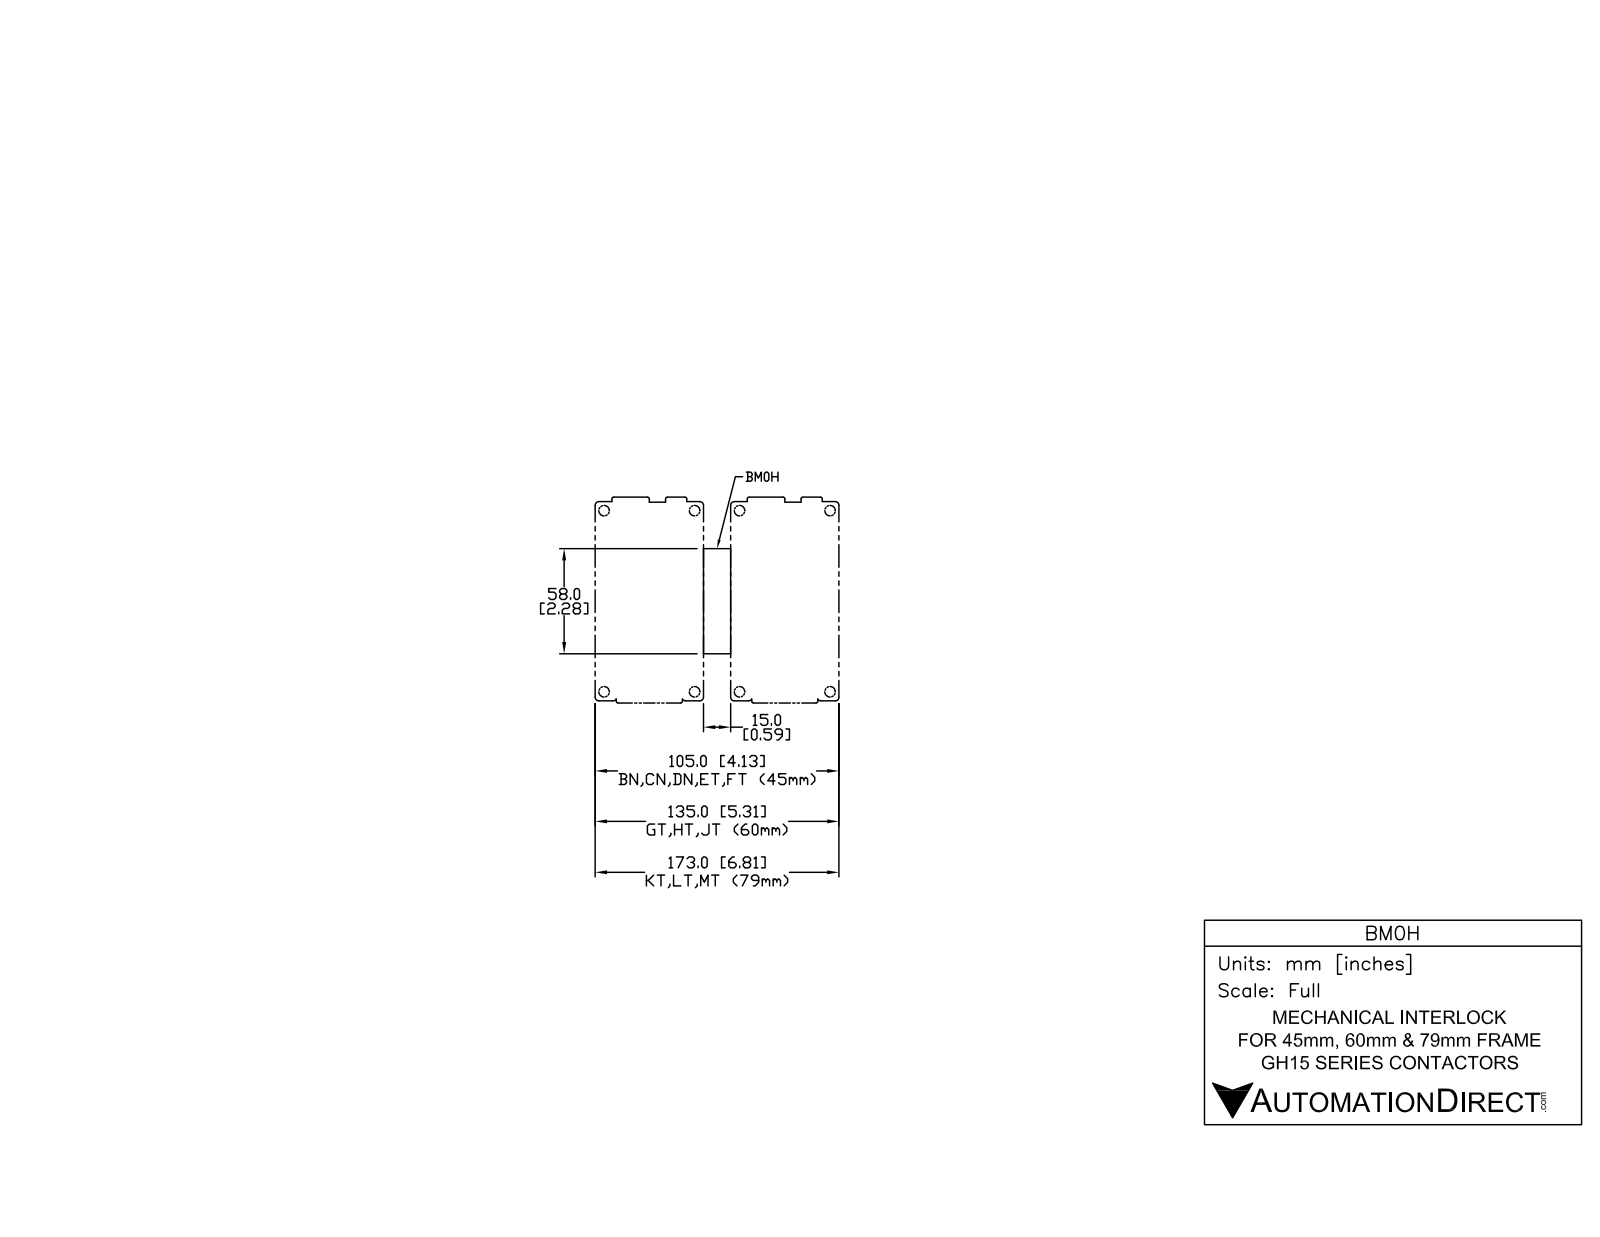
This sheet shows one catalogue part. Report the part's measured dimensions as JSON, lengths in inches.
{"part_name": "BM0H", "step_written_by": "SolidWorks 2009 (AUTOMOTIVE_DESIGN)", "units": "inches", "bodies": {"solids": 1, "faces": 82, "planar": 58, "cylindrical": 20, "other": 4}, "overall_size": [2.303, 1.929, 0.827], "volume_in3": 2.485, "surface_area_in2": 15.91, "round_bosses_or_shafts": [[0.276, 1], [0.118, 1]], "partial_cylinders_radius": [[0.02, 4], [0.206, 2], [0.207, 2]], "face_to_face_distances": [0.591, 1.929, 2.303, 0.118, 0.197, 0.472, 0.079, 0.394, 0.187, 0.276]}
